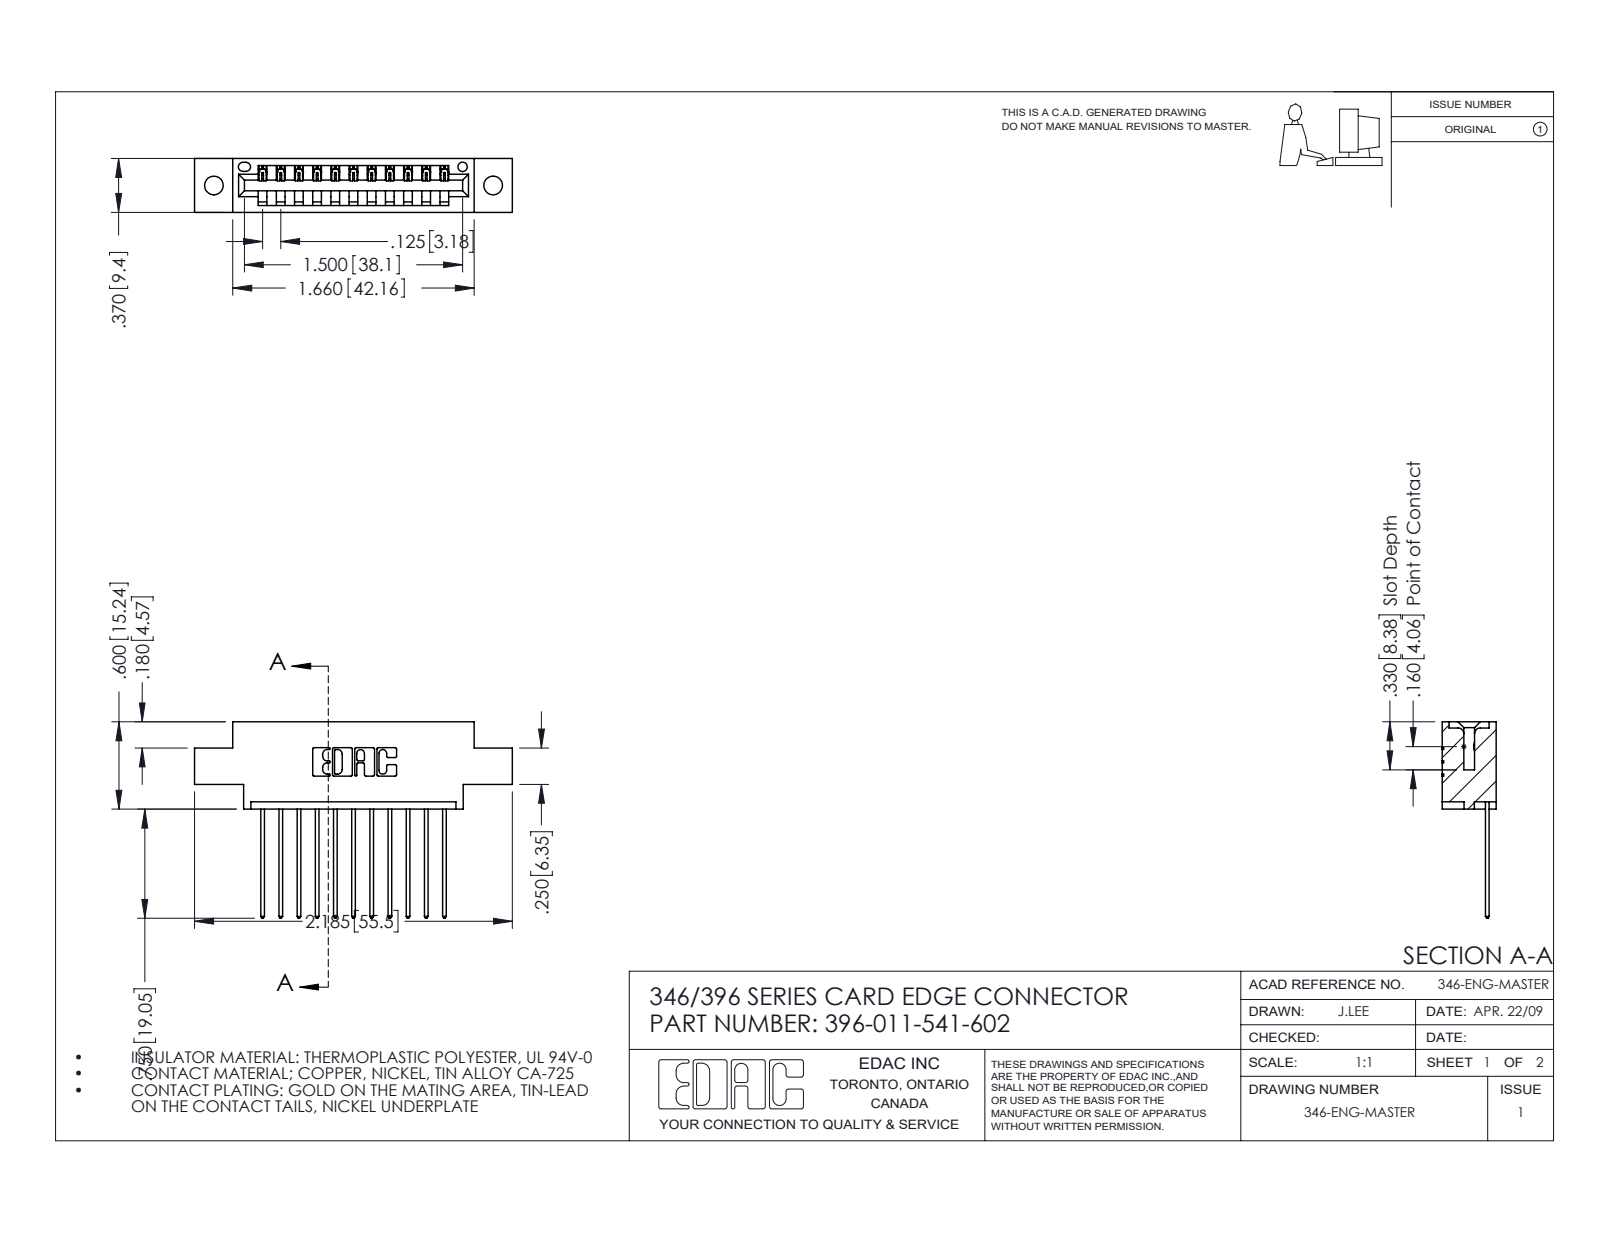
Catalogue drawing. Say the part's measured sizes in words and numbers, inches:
The part is named "345-292-001_345-293-141; 346 Part_0.170 Offset - 0.128 Dia; 396-011-541-602". Its 3-D file was written by "SolidWorks 2016 (CONFIG_CONTROL_DESIGN)". It is 12 solids with 764 faces: 520 planar, 244 cylindrical and 0 other. Overall it measures 2.185 by 1.35 by 0.37 inches. Its volume is 0.302 cubic inches and its surface area 9.224 square inches. Round holes: 2 of diameter 0.128, 1 of diameter 0.064. Partial cylindrical surfaces (rounded edges, fillets, slot ends): 22 of radius 0.006, 22 of radius 0.01, 22 of radius 0.01, 6 of radius 0.007, 6 of radius 0.031, 3 of radius 0.026, 2 of radius 0.031, 2 of radius 0.04. The main face-to-face distances are 0.25, 0.048, 0.322, 0.37, 0.072, 0.298, 0.025, 0.148, 0.222, 0.1. The hole center spacings are 0.246, 1.715, 1.92.
